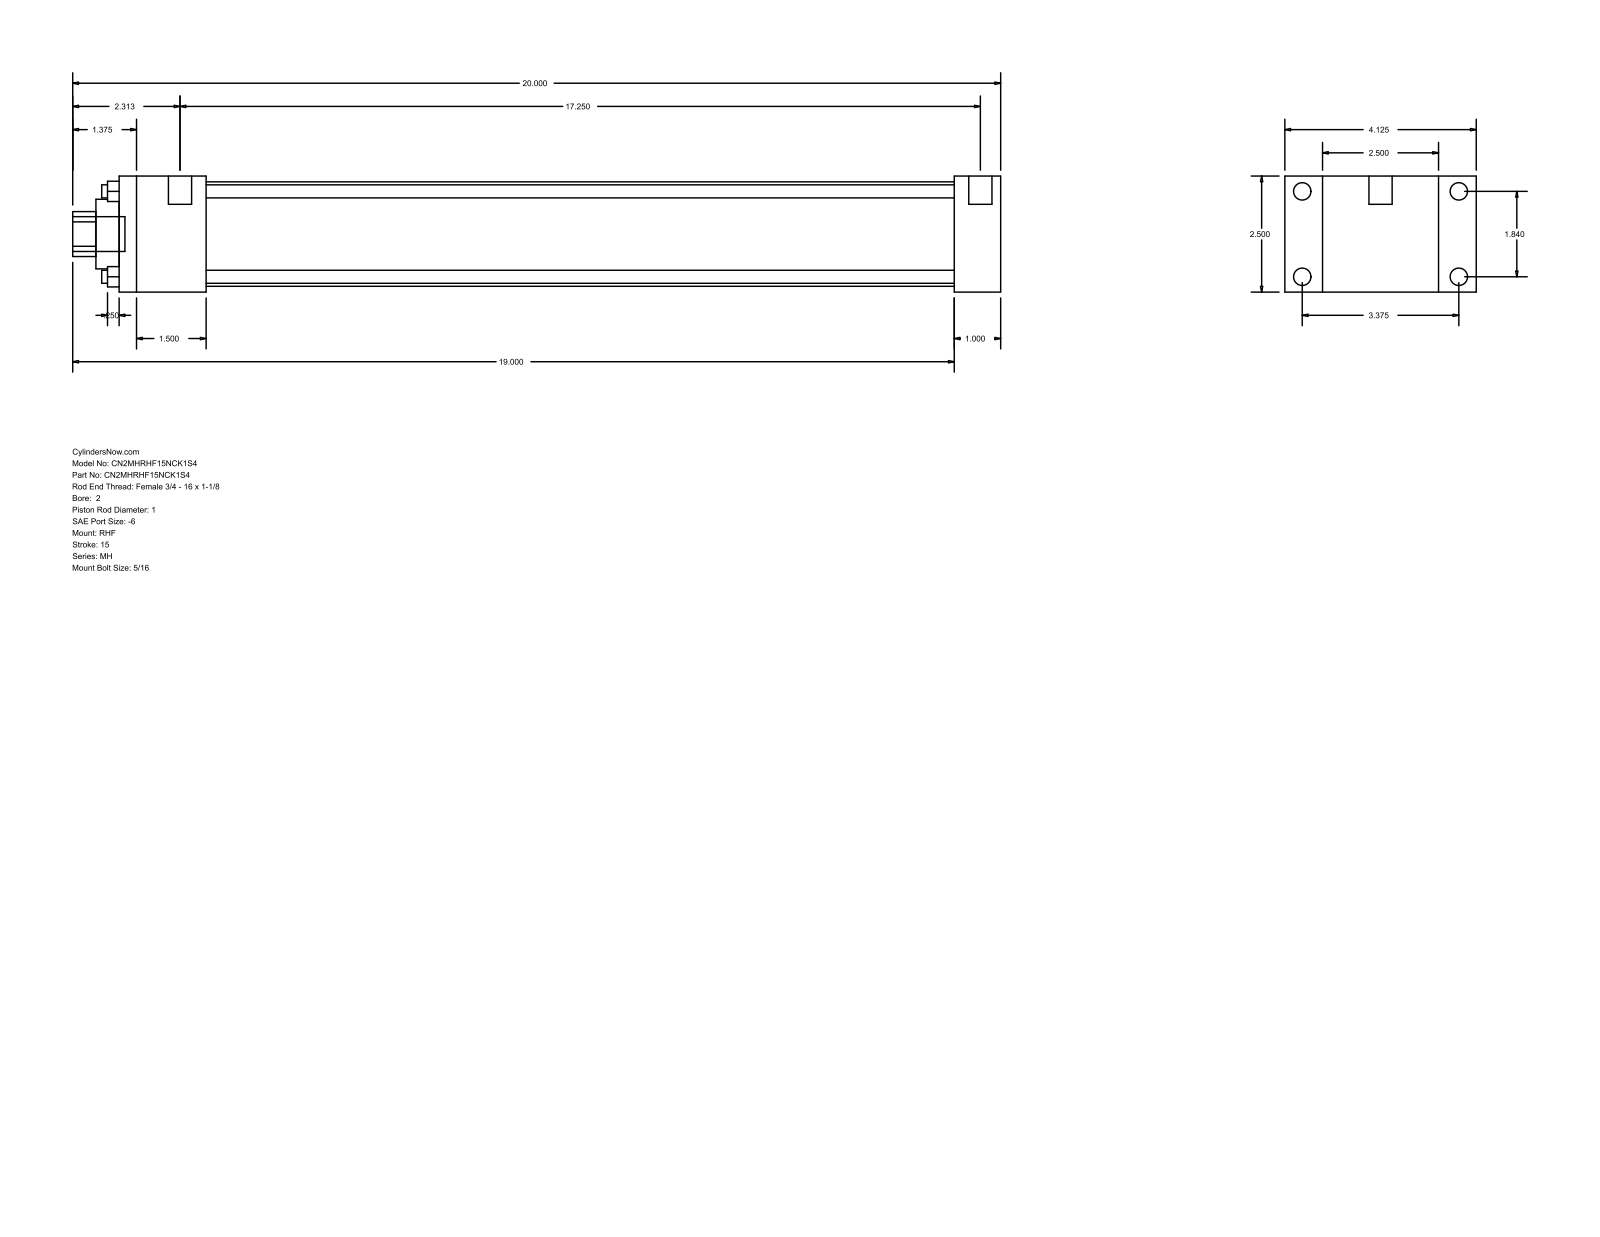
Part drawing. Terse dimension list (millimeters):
name: MH_RHF__0200_1
written by: GSSL Pune (CONFIG_CONTROL_DESIGN)
unit: mm
bodies: 0 solids, 88 faces (60 planar, 28 cylindrical, 0 other)
size: 508 × 104.78 × 63.5
holes: 4× ⌀7.14, 1× ⌀25.4, 1× ⌀38.1, 1× ⌀57.15
bosses: 4× ⌀9.53, 4× ⌀5.56, 2× ⌀12.7, 1× ⌀19.05
rounds: 1× R12.29
face distances: 63.5, 25.4, 20.64, 84.14, 482.6, 457.2, 104.78, 47.63, 409.57, 434.97
hole spacings: 33.05, 46.74, 66.1
